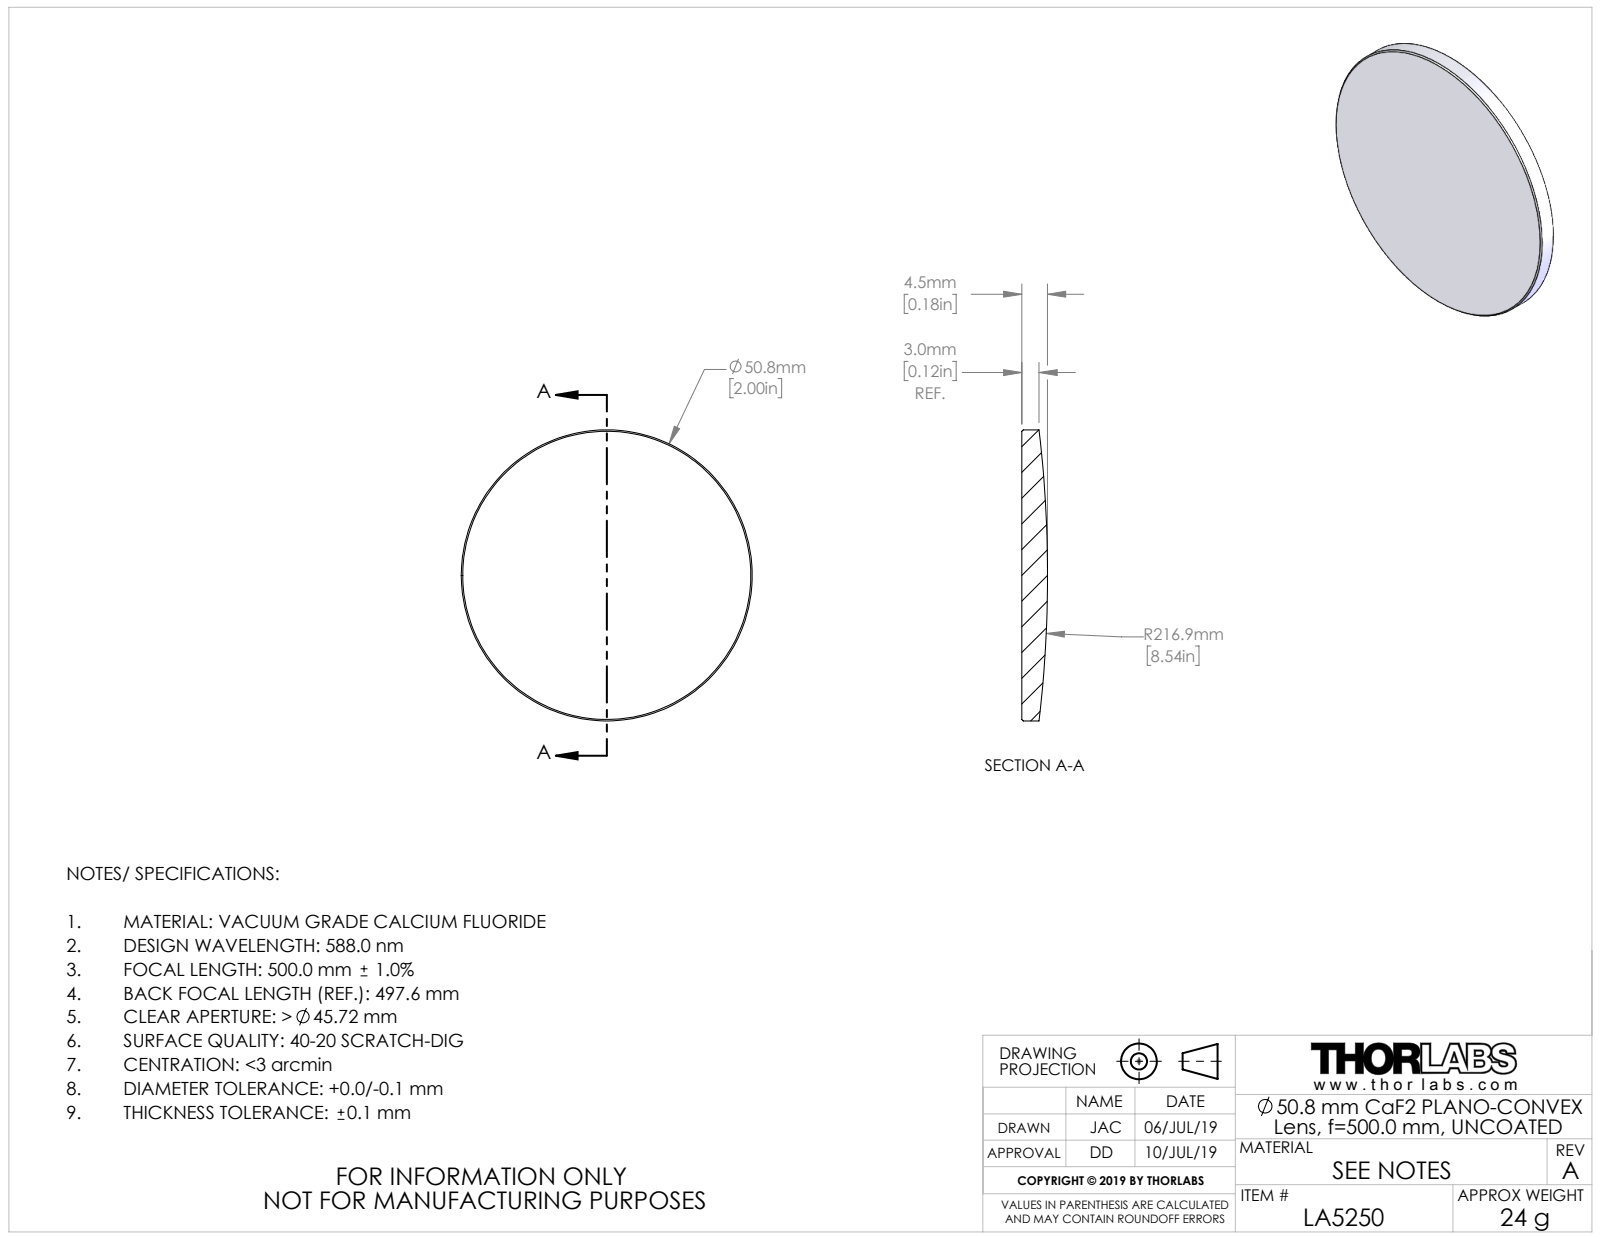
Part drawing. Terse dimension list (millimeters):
name: TTN188100-E0W
written by: SolidWorks 2018 (CONFIG_CONTROL_DESIGN)
unit: mm
bodies: 1 solid, 7 faces (1 planar, 2 cylindrical, 4 other)
size: 50.8 × 50.8 × 4.49
volume: 7 585 mm³; area: 4 516 mm²
bosses: 1× ⌀50.8
